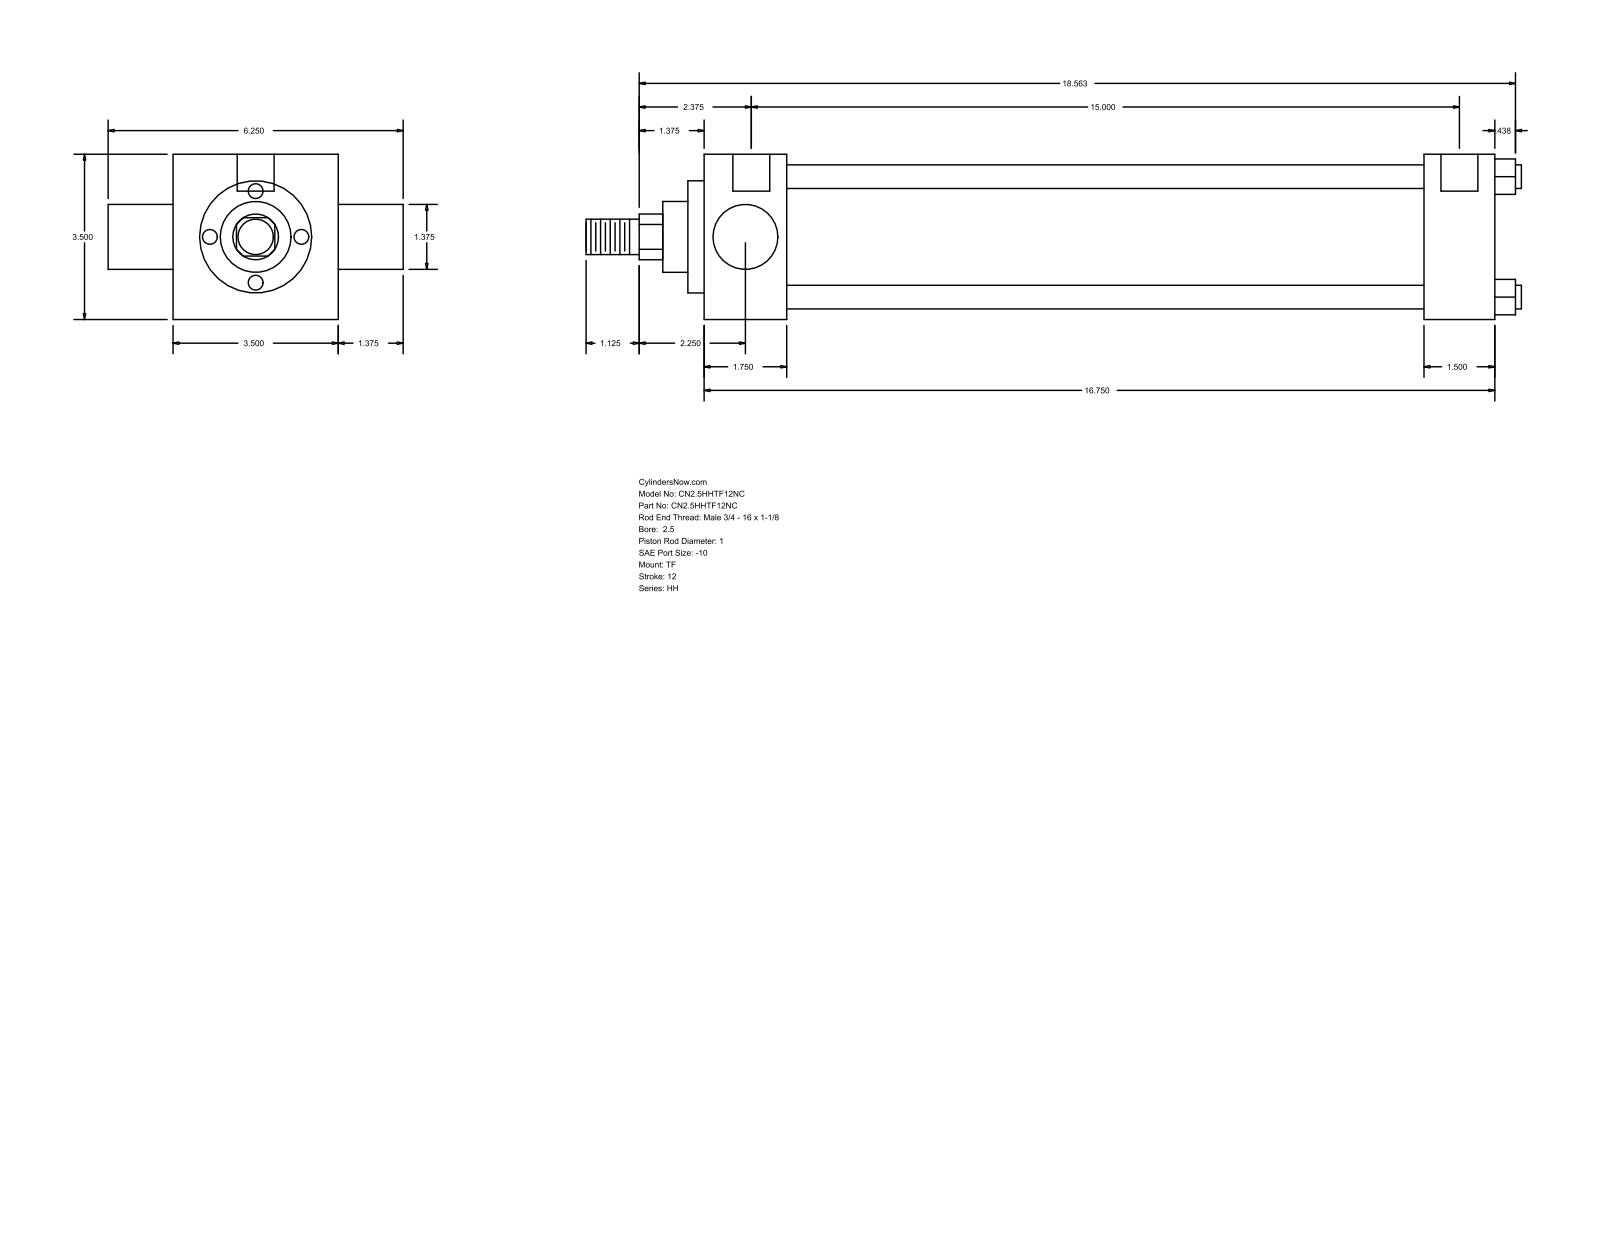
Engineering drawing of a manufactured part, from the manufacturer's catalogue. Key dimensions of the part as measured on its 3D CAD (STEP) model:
Part name (STEP PRODUCT): HH_TF__0250_1
STEP written by: GSSL Pune (CONFIG_CONTROL_DESIGN)
Units: millimetres
Bodies: 0 solids, 86 faces (61 planar, 25 cylindrical, 0 other)
Overall size (bounding box): 503.24 × 158.75 × 88.9
Round holes (diameter × count): ⌀5.56 ×3, ⌀19.84 ×2
Round bosses / shafts (diameter × count): ⌀12.7 ×4, ⌀73.03 ×1, ⌀60.33 ×1, ⌀38.1 ×1, ⌀34.92 ×1, ⌀25.4 ×1, ⌀19.05 ×1
Partial cylindrical surfaces — rounded edges, fillets, slot ends (radius × count): R12.29 ×1
Main face-to-face distances: 88.9, 425.46, 44.46, 381, 387.35, 342.89, 38.11, 34.93, 123.83, 8.73
Hole centre spacings: 1.59, 382.58, 380.99, 384.17
